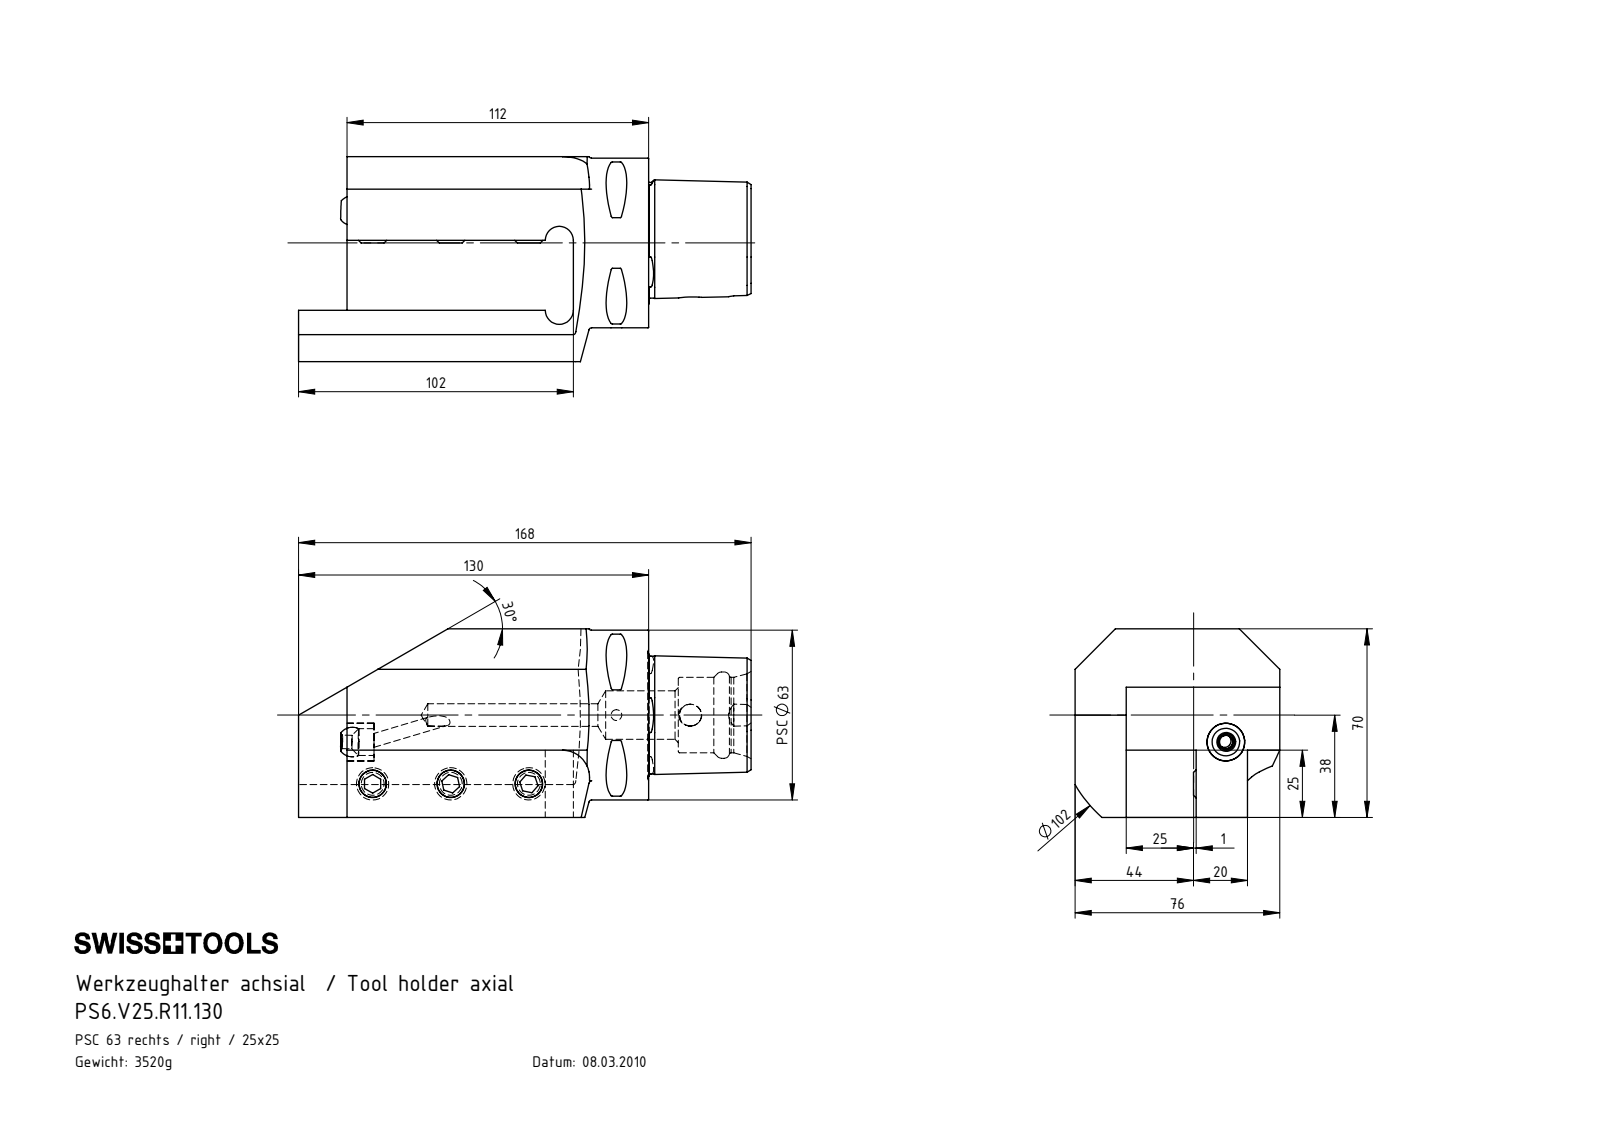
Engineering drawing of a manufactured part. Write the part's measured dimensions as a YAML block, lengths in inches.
part_name: "KU1-U14.001.012_1; KU1-U14.001.012; KU1-U14.001.012_2; ISO 4026 - M12 x 20 (+2 more)"
step_written_by: "SolidWorks 2017 (AUTOMOTIVE_DESIGN)"
units: inches
bodies: {solids: 7, faces: 228, planar: 68, cylindrical: 56, other: 104}
overall_size: [10.606, 10.606, 8.792]
volume: 405
surface_area: 413.1
round_holes:
  - {diameter: 0.402, count: 3}
  - {diameter: 0.197, count: 2}
  - {diameter: 0.157, count: 1}
  - {diameter: 0.319, count: 1}
  - {diameter: 0.331, count: 1}
  - {diameter: 0.394, count: 1}
  - {diameter: 0.551, count: 1}
  - {diameter: 0.709, count: 1}
  - {diameter: 1.102, count: 1}
  - {diameter: 1.26, count: 1}
round_bosses_or_shafts:
  - {diameter: 0.472, count: 3}
  - {diameter: 10.606, count: 1}
  - {diameter: 2.48, count: 1}
partial_cylinders:
  - {radius: 0.02, count: 8}
  - {radius: 0.205, count: 2}
  - {radius: 0.236, count: 1}
  - {radius: 0.394, count: 1}
  - {radius: 2.008, count: 1}
face_to_face_distances: [4.274, 1.772, 0.748, 0.984, 2.992, 2.244, 2.756, 0.472, 2.52, 8.083]
hole_center_spacings: [1.142, 0.615, 1.083, 1.626, 2.283, 2.567, 2.621, 3.645]
